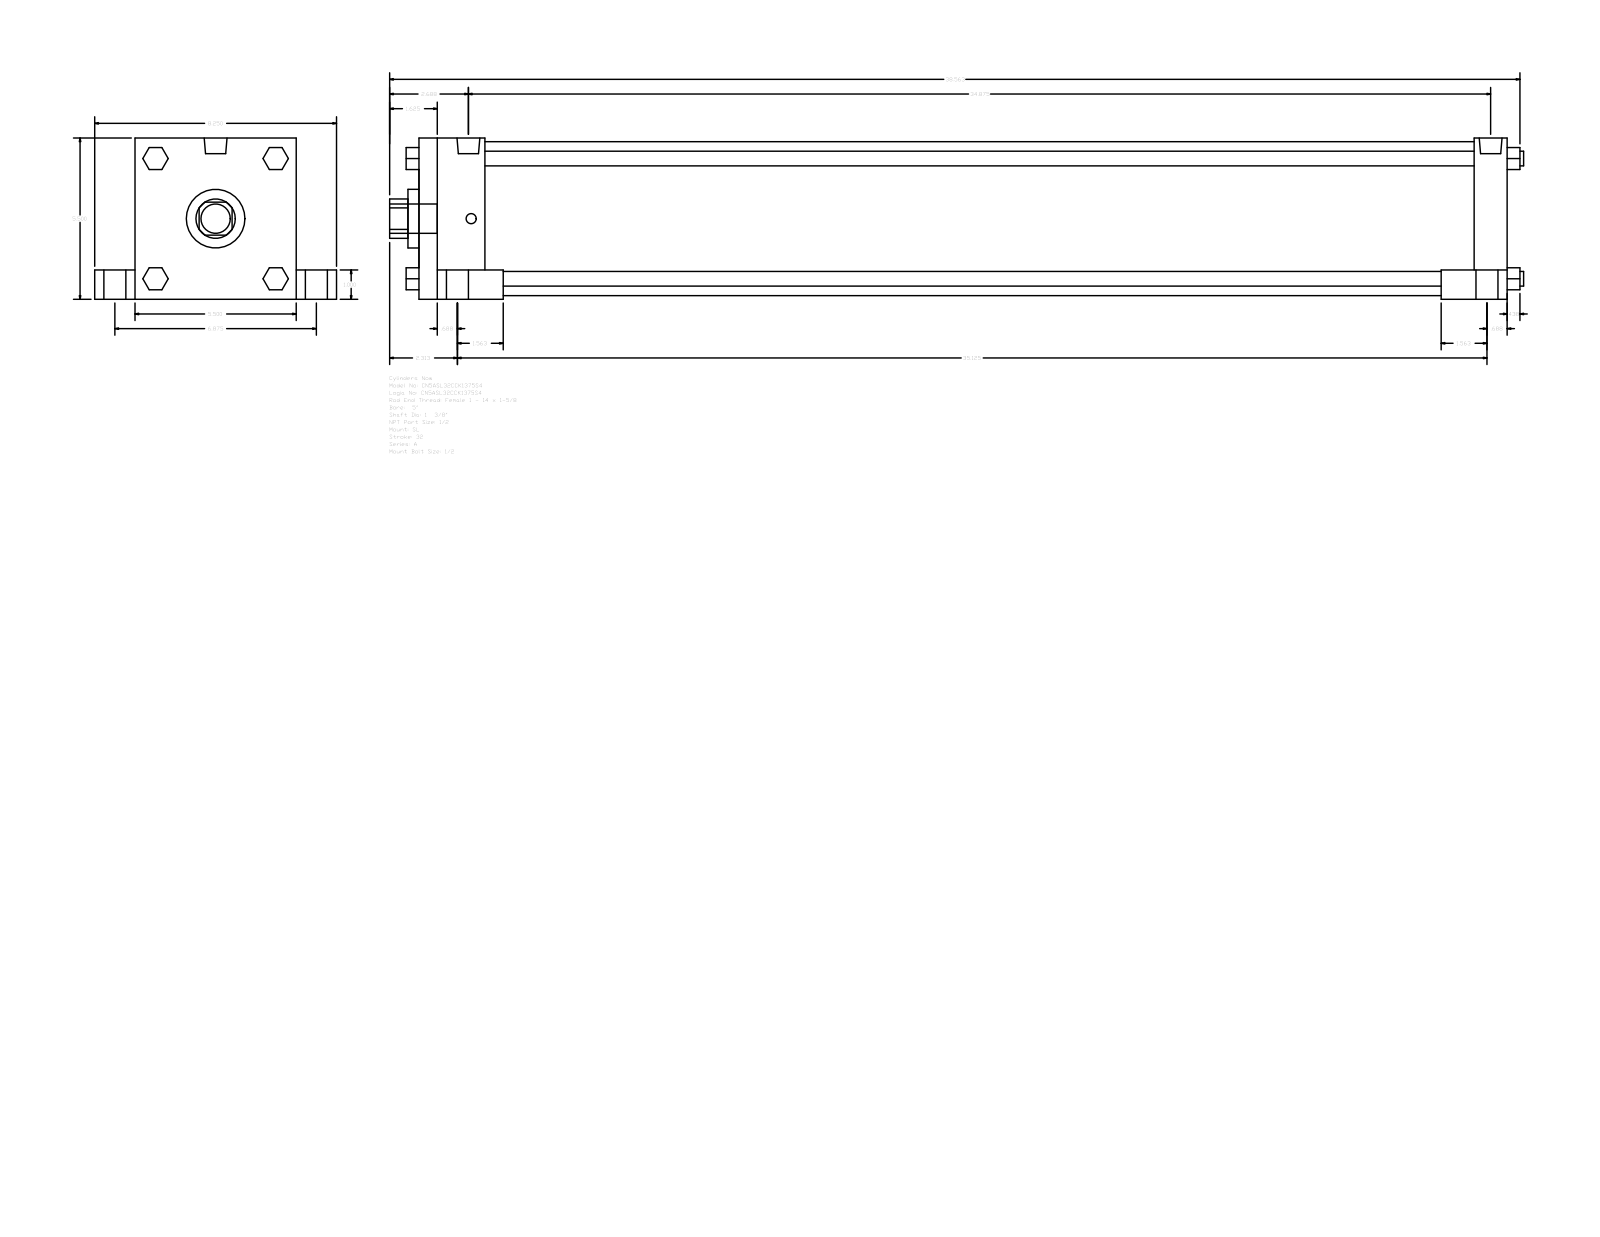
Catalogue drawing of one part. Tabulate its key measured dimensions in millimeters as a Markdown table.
| quantity | value |
| --- | --- |
| part name | A_SL__0500_1.375 |
| STEP written by | GSSL Pune (CONFIG_CONTROL_DESIGN) |
| units | millimeters |
| bodies | 0 solids, 150 faces (114 planar, 36 cylindrical, 0 other) |
| overall size | 982.66 × 209.55 × 139.7 |
| round holes (diameter × count) | 34.92 × 1, 50.8 × 1, 133.35 × 1 |
| round bosses / shafts (diameter × count) | 25.4 × 5, 19.05 × 4, 12.7 × 4, 8.73 × 4, 19.77 × 2 |
| partial cylindrical surfaces (radius × count) | 17.06 × 1 |
| main face-to-face distances | 139.7, 942.98, 57.15, 885.83, 25.4, 114.3, 34.93, 174.63, 28.58, 914.4 |
